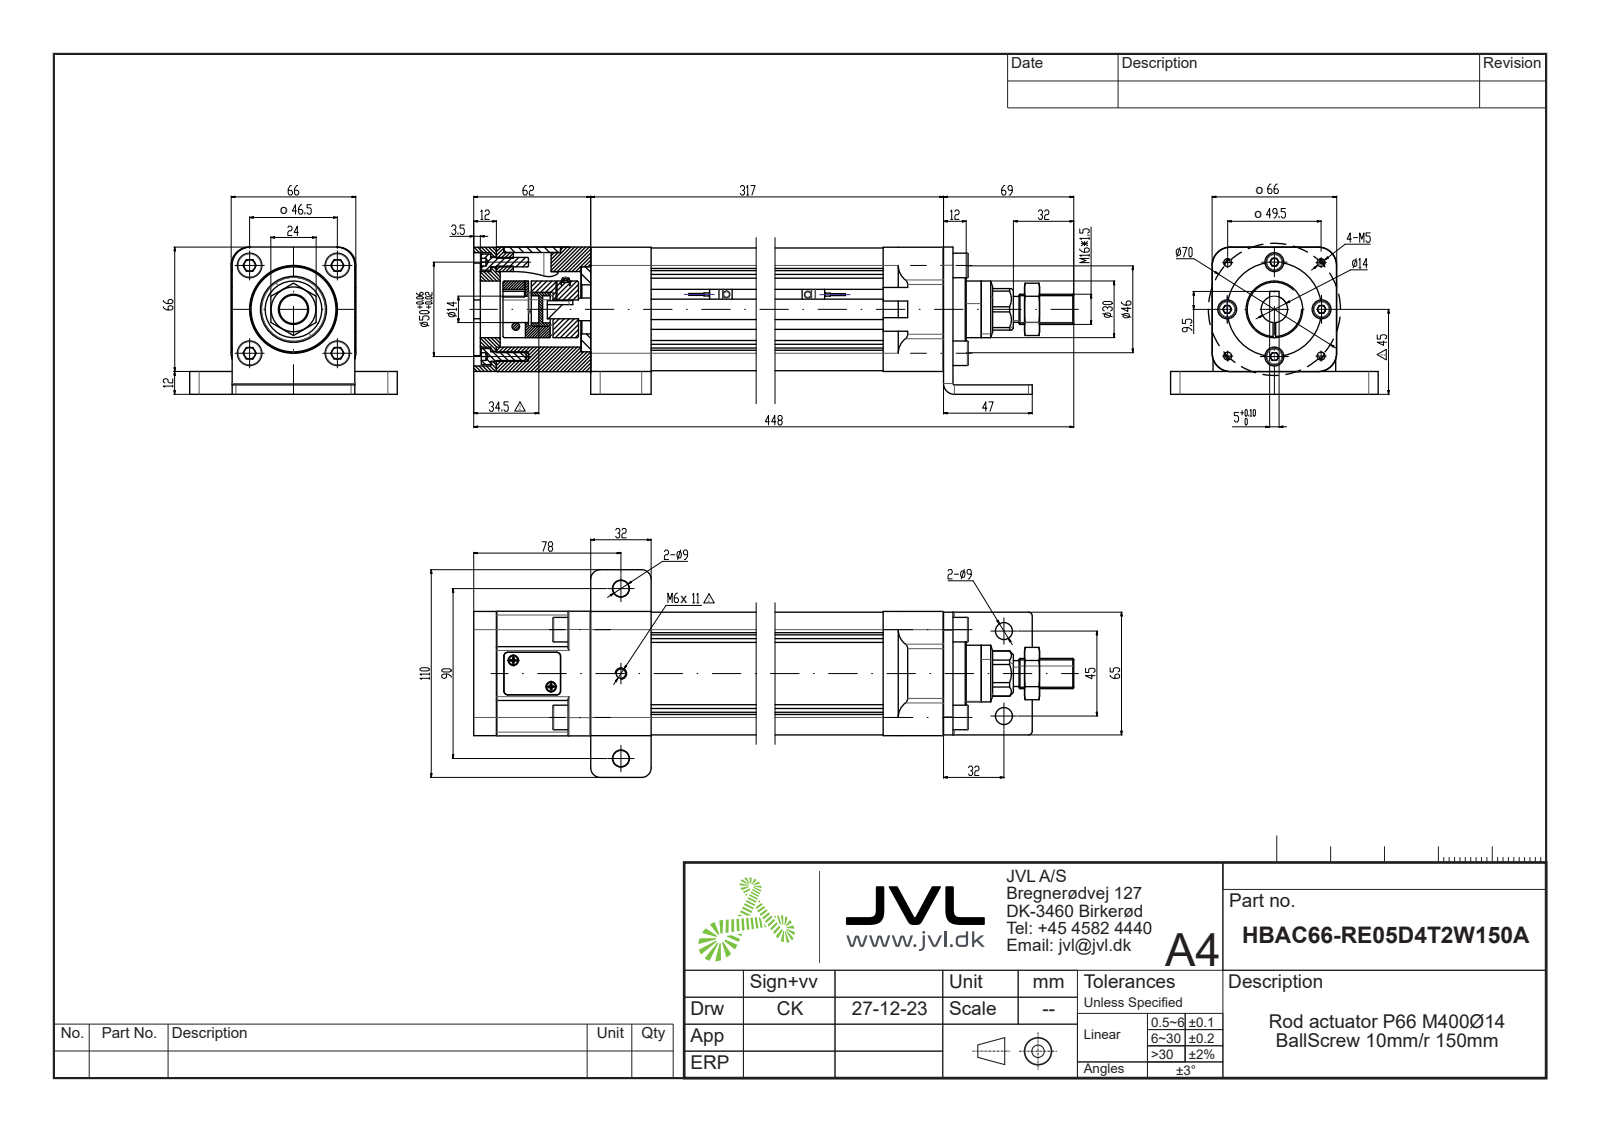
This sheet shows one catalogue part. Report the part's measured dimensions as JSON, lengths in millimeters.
{"part_name": "countersunk flat head cross recess screw_iso_ISO 7046-1 - M2.5 x 6 - Z - 6N; HBAC66-RC05D4T2W150A (insides); ZL-50-1 -____-14; PDU-030-14_YNM-01-PDU-30 (+8 more)", "step_written_by": "SolidWorks 2023 (AUTOMOTIVE_DESIGN)", "units": "millimeters", "bodies": {"solids": 66, "faces": 2371, "planar": 912, "cylindrical": 743, "other": 716}, "overall_size": [448, 110, 78], "volume_mm3": 1211000, "surface_area_mm2": 436377, "round_holes": [[4.2, 14], [5.5, 10], [9, 8], [5, 4], [6.7, 4], [6.8, 4], [8.4, 4], [10, 4], [12.5, 4], [2.05, 2], [2.5, 2], [2.9, 2]], "round_bosses_or_shafts": [[8.5, 10], [5, 10], [12, 5], [13, 4], [8, 4], [10, 3], [6, 2], [5.5, 2]], "partial_cylinders_radius": [[0.2, 40], [0.5, 20], [9, 17], [2, 15], [1, 12], [9.65, 10], [3, 8], [0.1, 6]], "face_to_face_distances": [5, 65, 32, 0.4, 65.4, 4.5, 60.5, 285, 60.9, 61], "hole_center_spacings": [17.73, 23.32, 24.75, 37.98, 39.83, 40.72, 48.02, 53.56]}
